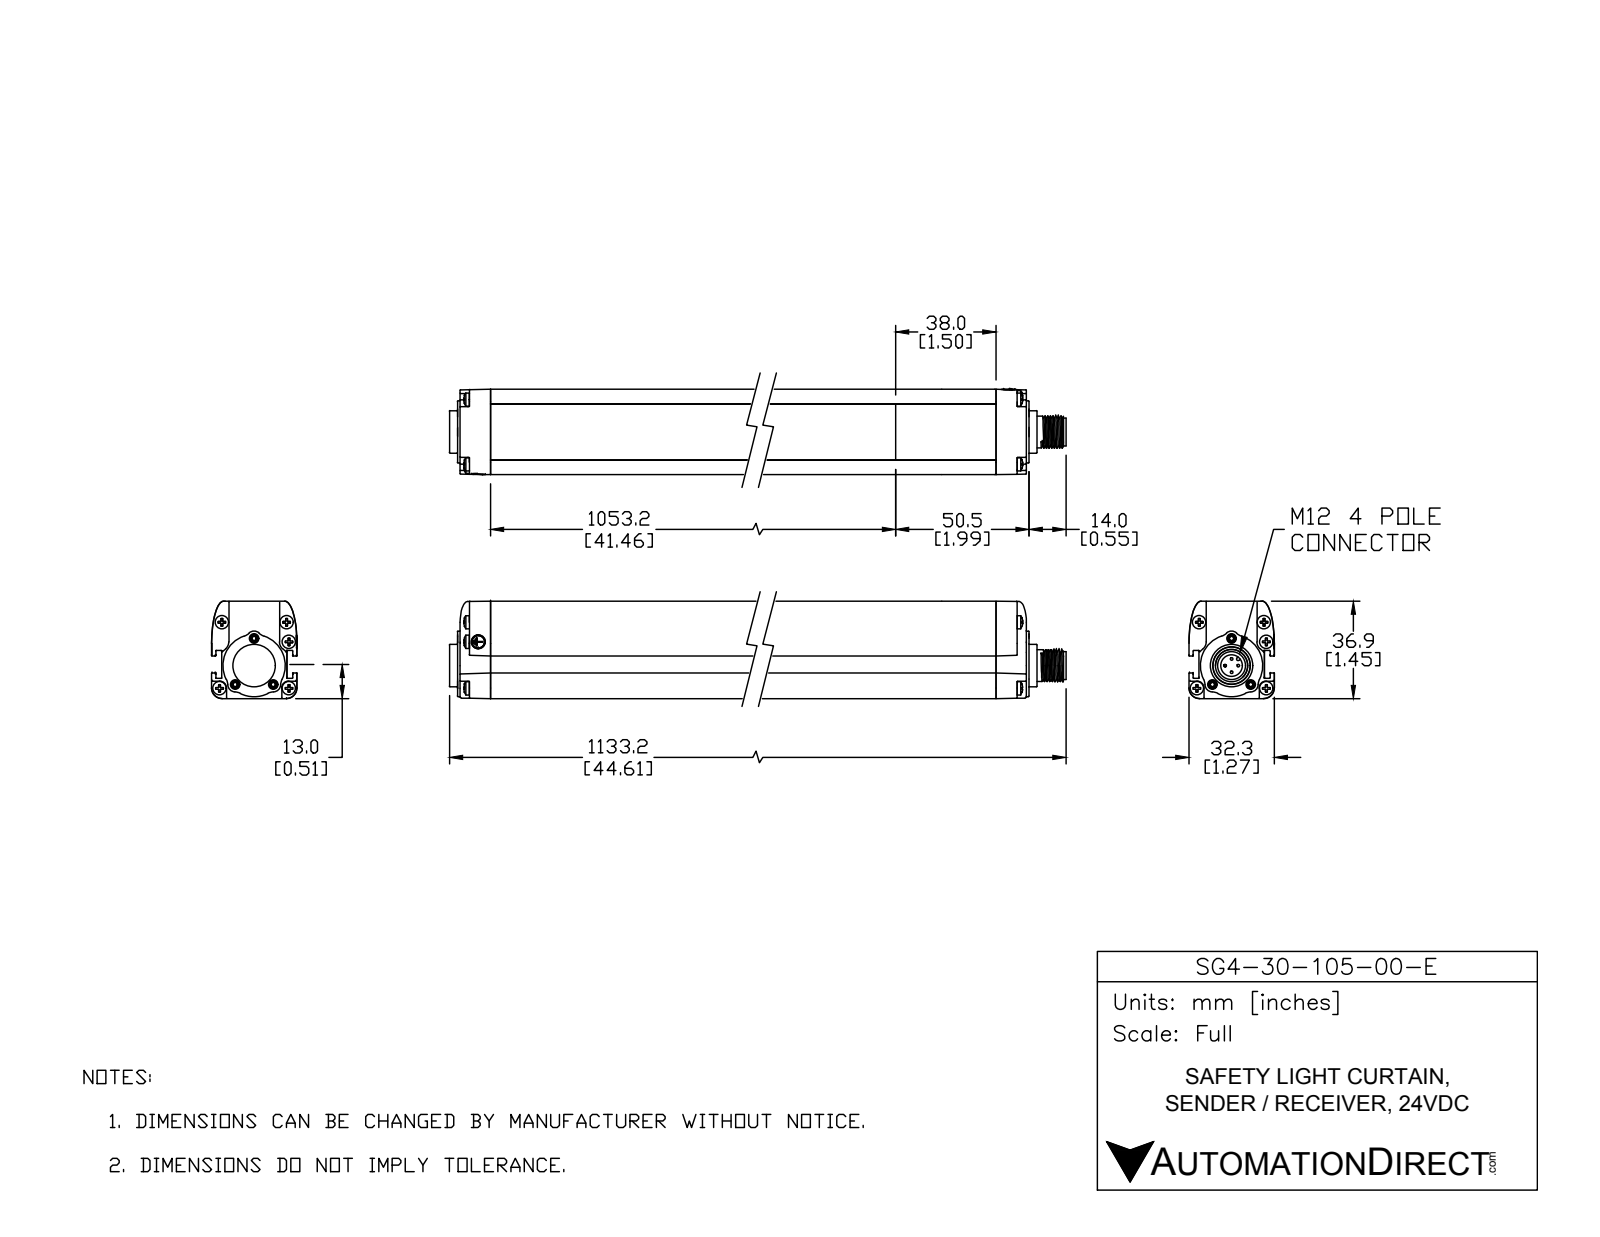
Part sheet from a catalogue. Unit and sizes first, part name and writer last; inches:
Units: inches
Overall size (bounding box): 44.615 × 2.48 × 2.055
Round holes (diameter × count): ⌀0.106 ×6, ⌀0.209 ×6, ⌀0.081 ×4, ⌀0.165 ×4, ⌀0.26 ×4, ⌀0.059 ×3, ⌀0.142 ×3, ⌀0.323 ×1, ⌀0.376 ×1, ⌀0.433 ×1, ⌀0.563 ×1
Round bosses / shafts (diameter × count): ⌀0.197 ×10, ⌀0.394 ×4, ⌀0.039 ×4, ⌀0.185 ×2, ⌀0.63 ×1, ⌀0.55 ×1, ⌀0.472 ×1, ⌀0.413 ×1
Partial cylindrical surfaces — rounded edges, fillets, slot ends (radius × count): R0.008 ×148, R0.004 ×120, R0.006 ×18, R0.106 ×18, R0.118 ×8, R0.197 ×7, R0.11 ×3, R0.016 ×2
Main face-to-face distances: 0.079, 1.272, 1.429, 0.15, 1.122, 1.35, 0.157, 0.972, 0.333, 0.063
Hole centre spacings: 0.569, 41.387, 0.402, 0.24, 0.293, 0.52, 0.541, 0.619
Volume: 71.13 in³ · Surface area: 432 in²
Bodies: 29 solids, 1674 faces (410 planar, 591 cylindrical, 673 other)
Part name (STEP PRODUCT): SG4-30-105-OO-E
STEP written by: SolidWorks 2017 (AUTOMOTIVE_DESIGN)
